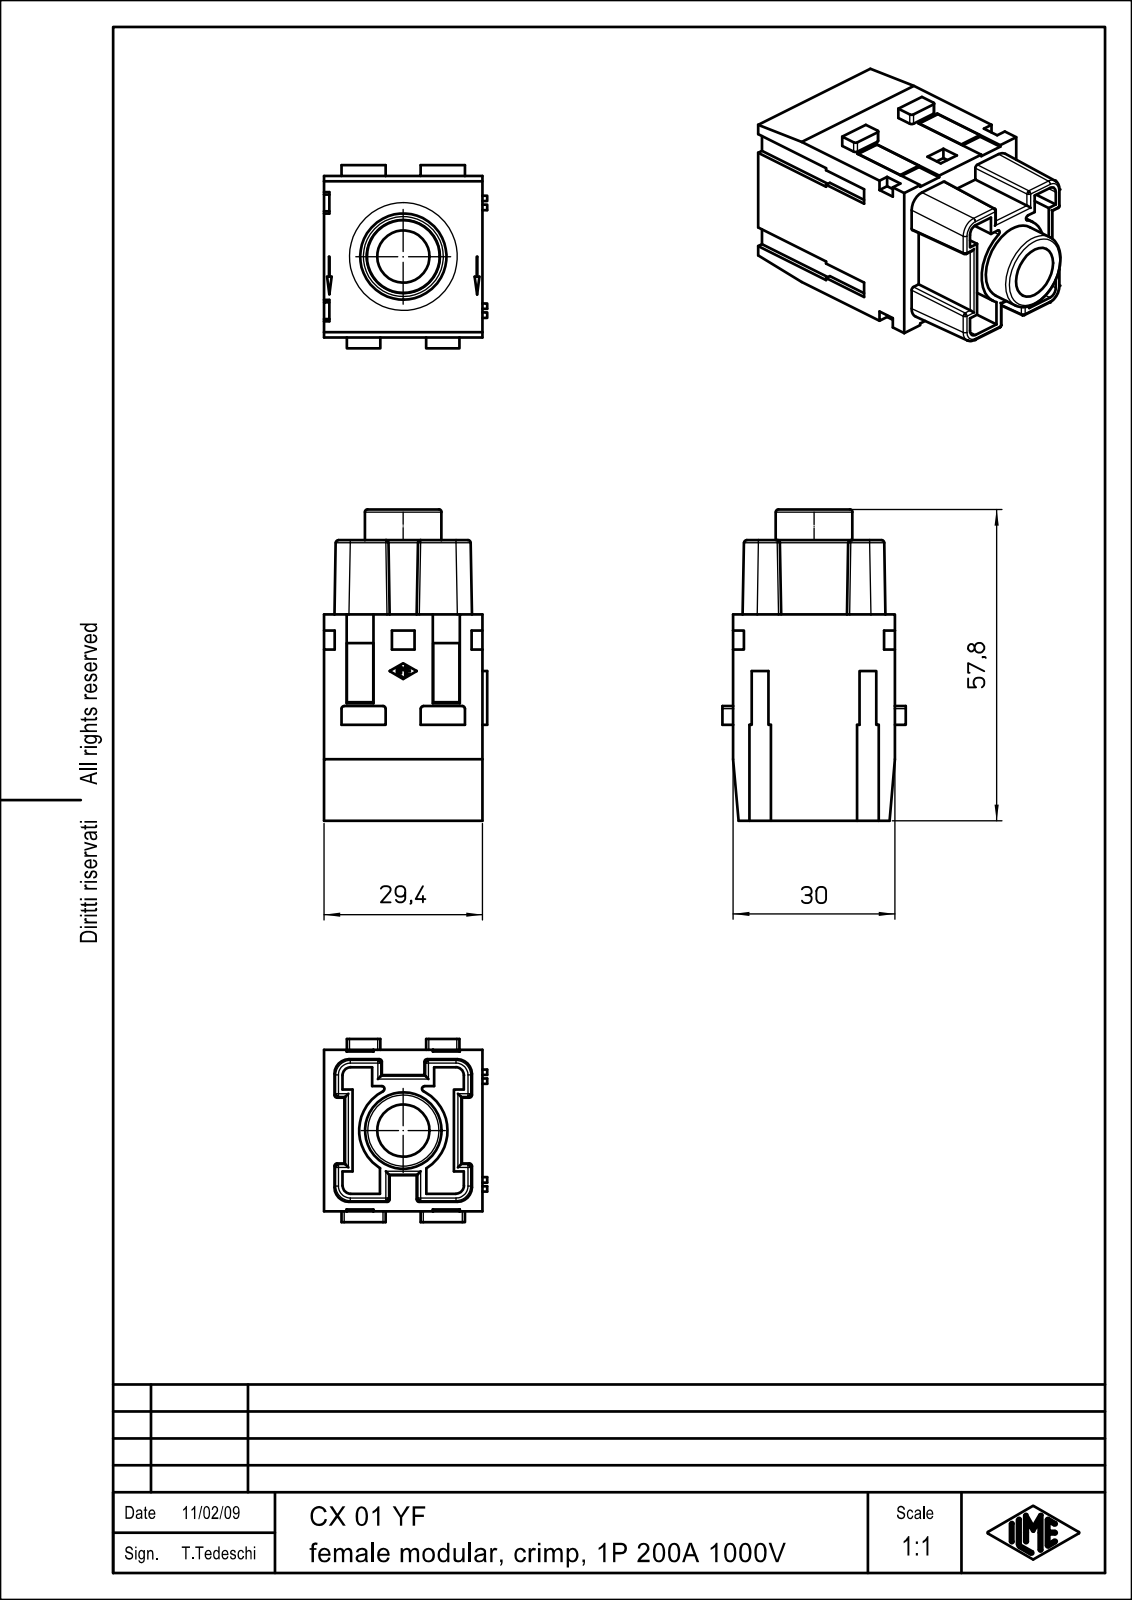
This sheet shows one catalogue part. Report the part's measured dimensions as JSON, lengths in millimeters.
{"part_name": "CX_01_YF", "step_written_by": "CoCreate Modeling 16.00A 16-Aug-2008 (C) Parametric Technology GmbH (AUTOMOTIVE_DESIGN)", "units": "millimeters", "bodies": {"solids": 1, "faces": 348, "planar": 232, "cylindrical": 70, "other": 46}, "overall_size": [57.8, 34, 30.3], "volume_mm3": 27473, "surface_area_mm2": 13727, "round_holes": [[9.7, 1], [16, 1], [20.5, 1]], "round_bosses_or_shafts": [[14.2, 1]], "partial_cylinders_radius": [[0.5, 28], [0.1, 14], [1.5, 4], [2.7, 4], [8.2, 1], [8.5, 1]], "face_to_face_distances": [29.4, 30, 38.3, 1.85, 5.3, 24.1, 8.5, 17.5, 3.25, 1]}
